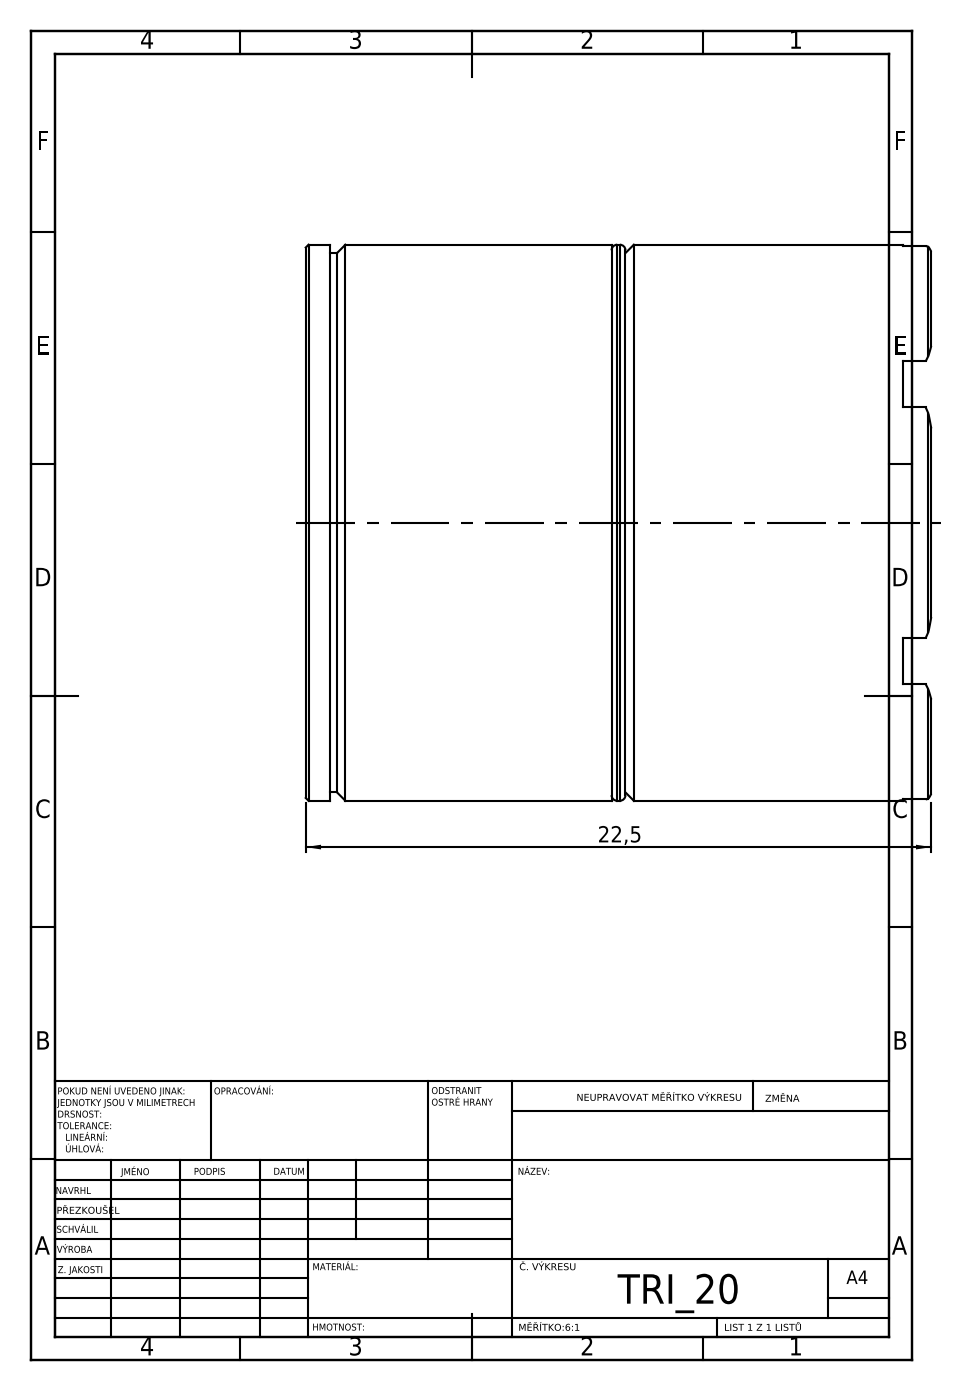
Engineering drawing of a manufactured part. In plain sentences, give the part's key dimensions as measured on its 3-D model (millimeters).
Its 3-D file was written by "SolidWorks 2019 (CONFIG_CONTROL_DESIGN)". It is 2 solids with 53 faces: 24 planar, 12 cylindrical and 17 other. Overall it measures 22.5 by 20 by 20 millimeters. Its volume is 6 920 cubic millimeters and its surface area 2 766 square millimeters. Round bosses or shafts: 1 of diameter 20, 1 of diameter 19.4. The main face-to-face distances are 11, 11.5, 0.5, 10, 10.5, 21.5, 18.2, 20.63, 10.63, 10.13.
